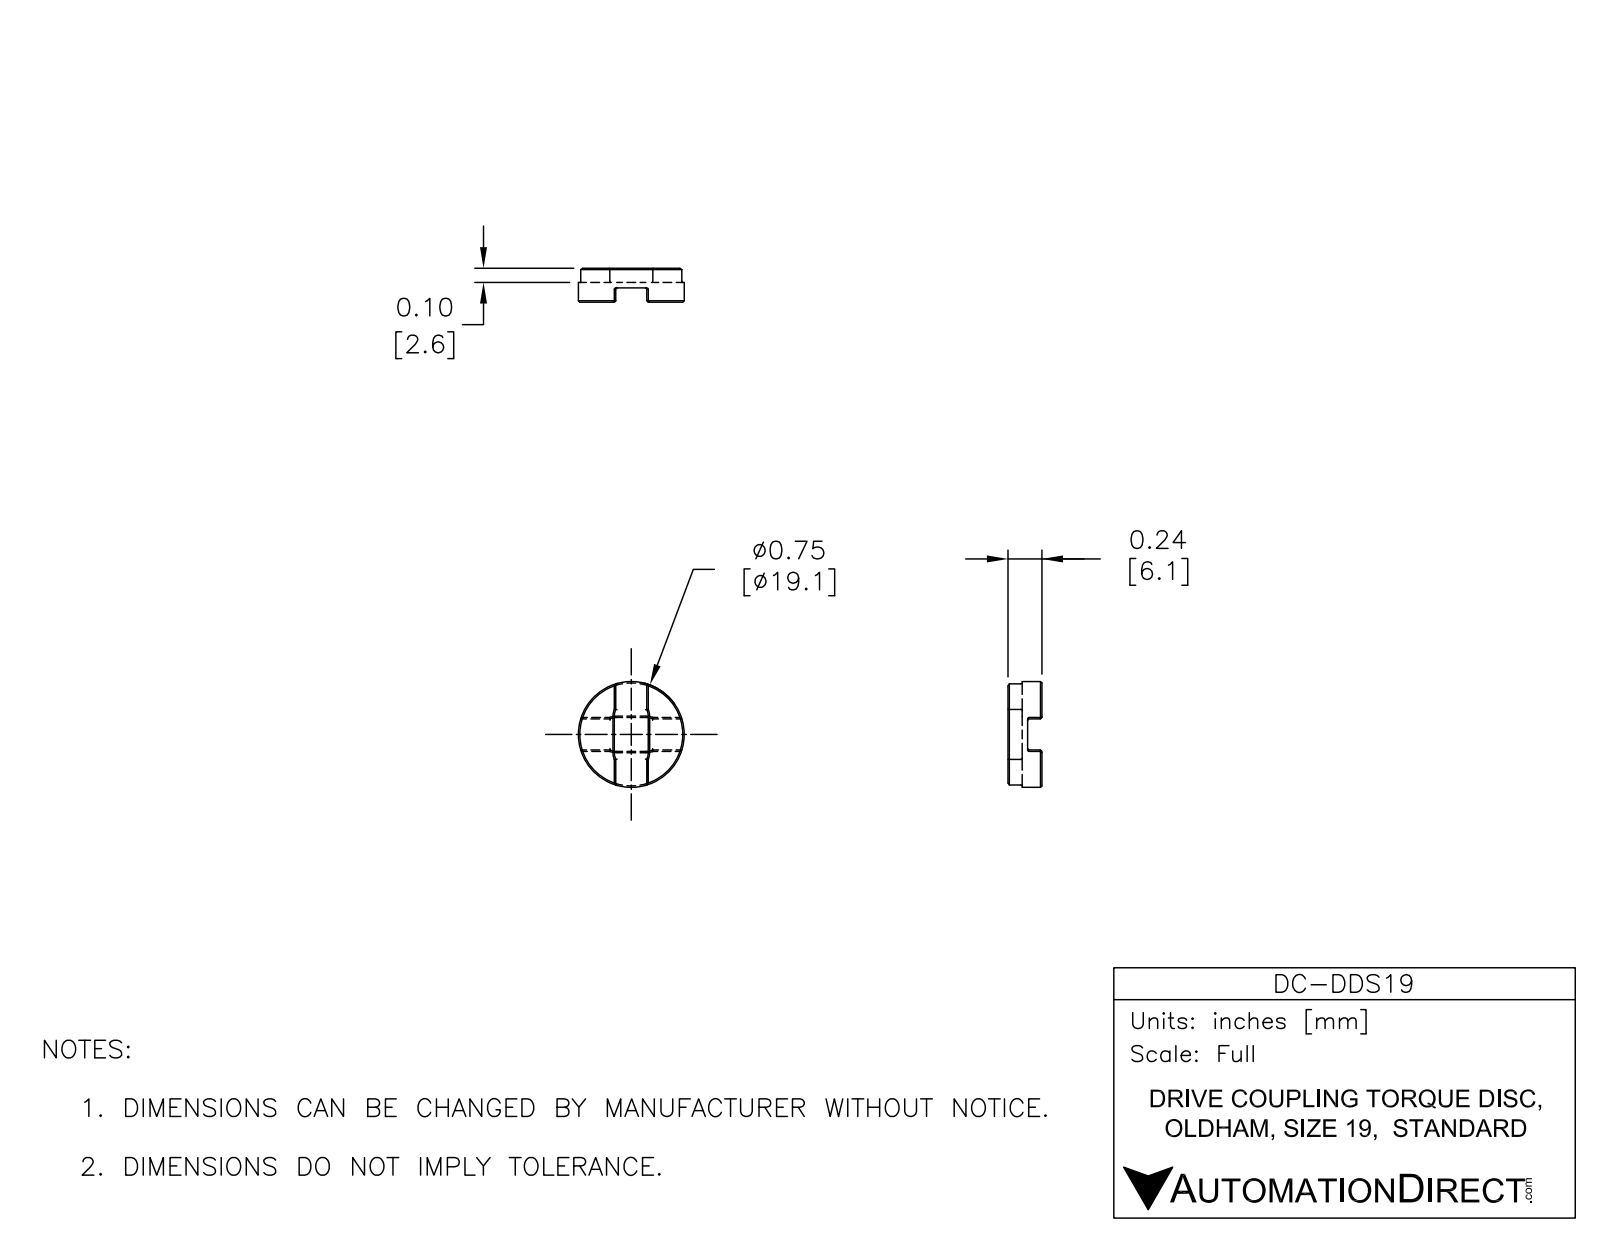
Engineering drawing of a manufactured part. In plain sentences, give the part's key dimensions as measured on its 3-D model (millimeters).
The part is named "DC-DDS19". Its 3-D file was written by "SolidWorks 2015 (AUTOMOTIVE_DESIGN)". It is 1 solid with 97 faces: 46 planar, 30 cylindrical and 21 other. Overall it measures 19.1 by 19.1 by 6.12 millimeters. Its volume is 1 188 cubic millimeters and its surface area 1 036 square millimeters. Round bosses or shafts: 1 of diameter 19.1. Partial cylindrical surfaces (rounded edges, fillets, slot ends): 16 of radius 0.25, 8 of radius 3.17. The main face-to-face distances are 6.12, 3.56, 2.56, 2.57, 0.99, 3.55, 5.87, 5.62, 8.36, 7.94.
